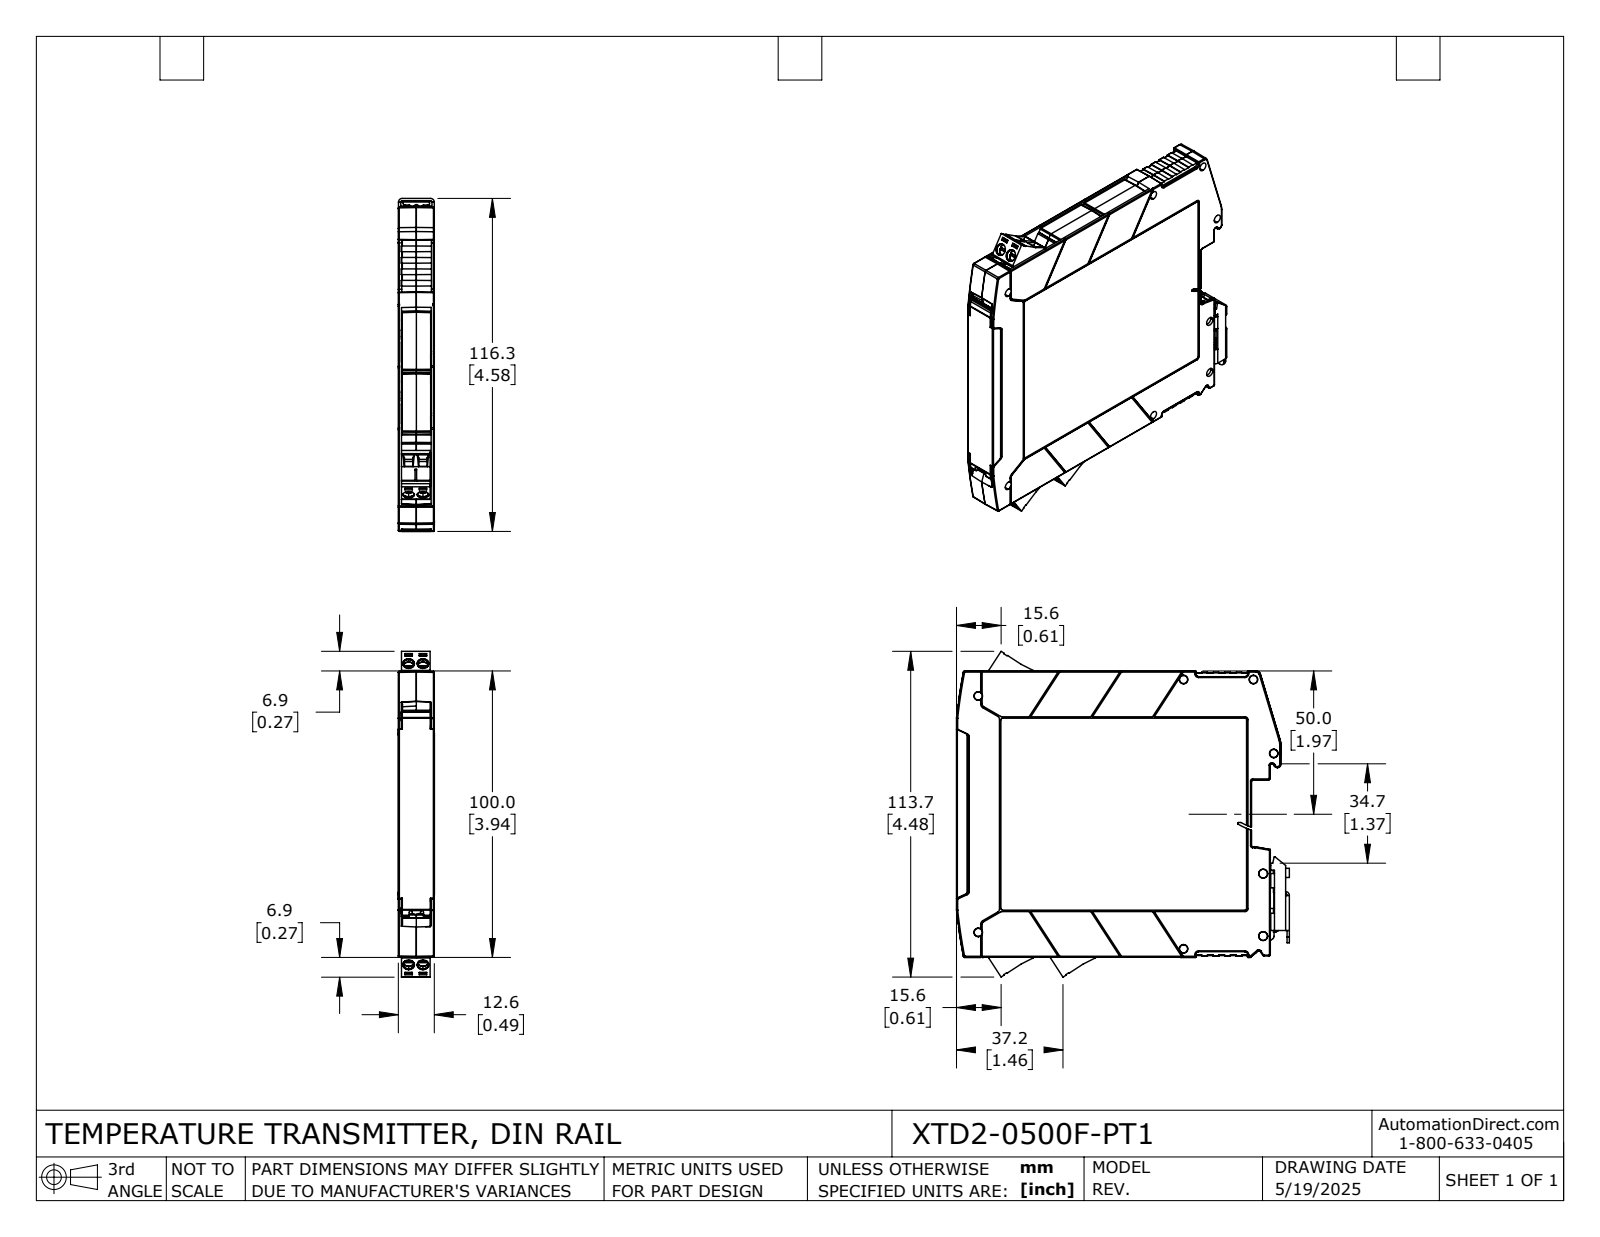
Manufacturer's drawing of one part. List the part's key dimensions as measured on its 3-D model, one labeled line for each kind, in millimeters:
Part name (STEP PRODUCT): XTD2-0500F-PT1
STEP written by: SolidWorks 2024 (AUTOMOTIVE_DESIGN)
Units: millimetres
Bodies: 14 solids, 3337 faces (1910 planar, 596 cylindrical, 831 other)
Overall size (bounding box): 116.3 × 113.7 × 12.6
Volume: 39 490 mm³ · Surface area: 65 480 mm²
Round holes (diameter × count): ⌀1.6 ×6, ⌀2.8 ×6, ⌀3.9 ×6, ⌀4 ×6
Round bosses / shafts (diameter × count): ⌀4 ×6, ⌀2.5 ×6, ⌀1.5 ×2, ⌀1.3 ×2
Partial cylindrical surfaces — rounded edges, fillets, slot ends (radius × count): R0.2 ×89, R0.3 ×78, R0.5 ×71, R1 ×22, R0.1 ×20, R0.4 ×13, R0.2 ×12, R0.7 ×8
Main face-to-face distances: 1.2, 11.3, 12.5, 10.1, 1.1, 11.5, 10.2, 0.8, 5, 6.3
Hole centre spacings: 5, 11.8, 12.8, 18.1, 18.8
